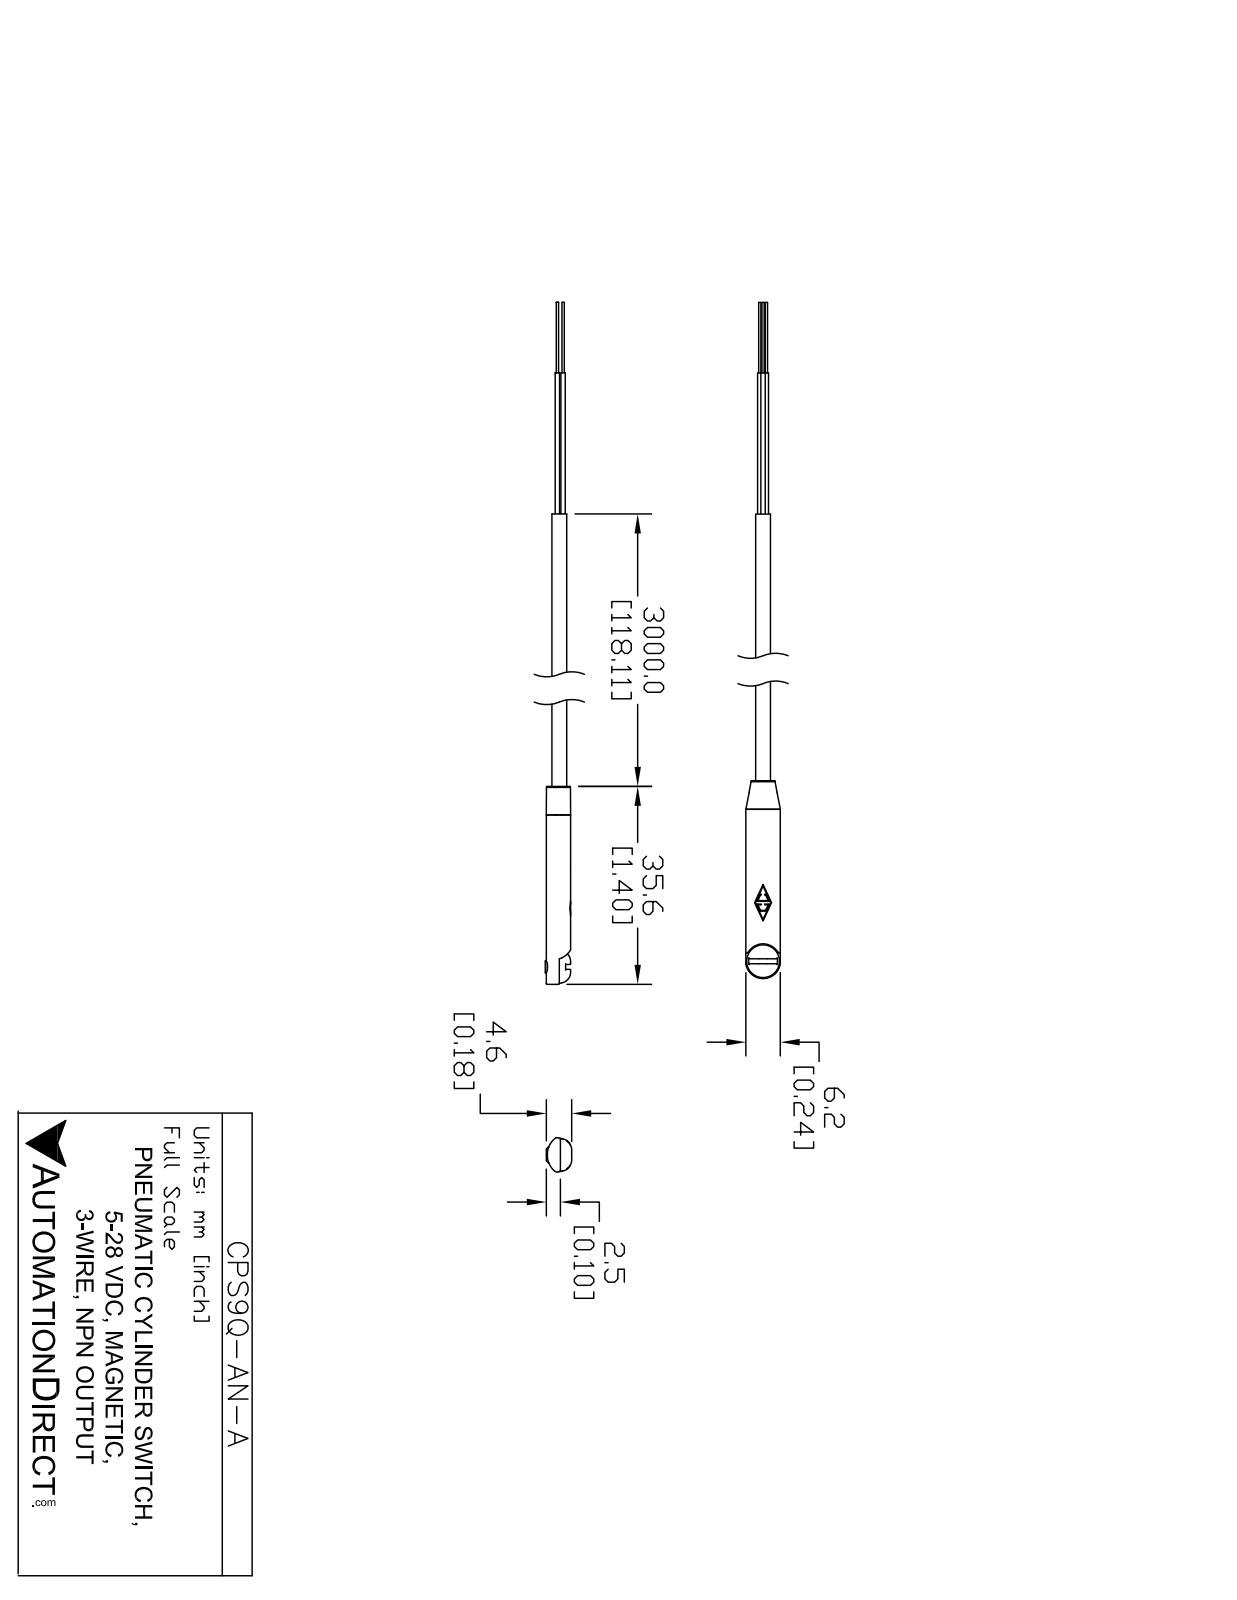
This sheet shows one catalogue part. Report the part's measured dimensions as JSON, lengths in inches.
{"part_name": "CPS9Q-AN-A", "step_written_by": "SolidWorks 2014 (AUTOMOTIVE_DESIGN)", "units": "inches", "bodies": {"solids": 3, "faces": 171, "planar": 79, "cylindrical": 50, "other": 42}, "overall_size": [7.17, 0.246, 0.18], "volume_in3": 0.084, "surface_area_in2": 2.846, "round_holes": [[0.032, 1]], "round_bosses_or_shafts": [[0.031, 3], [0.016, 3], [0.105, 1]], "partial_cylinders_radius": [[0.005, 4], [0.08, 3], [0.025, 2], [0.06, 2], [0.075, 2], [0.056, 1], [0.069, 1], [0.124, 1]], "face_to_face_distances": [0.172, 0.02, 0.152, 0.035, 0.015, 0.137, 0.045, 0.08, 0.06, 0.092]}
